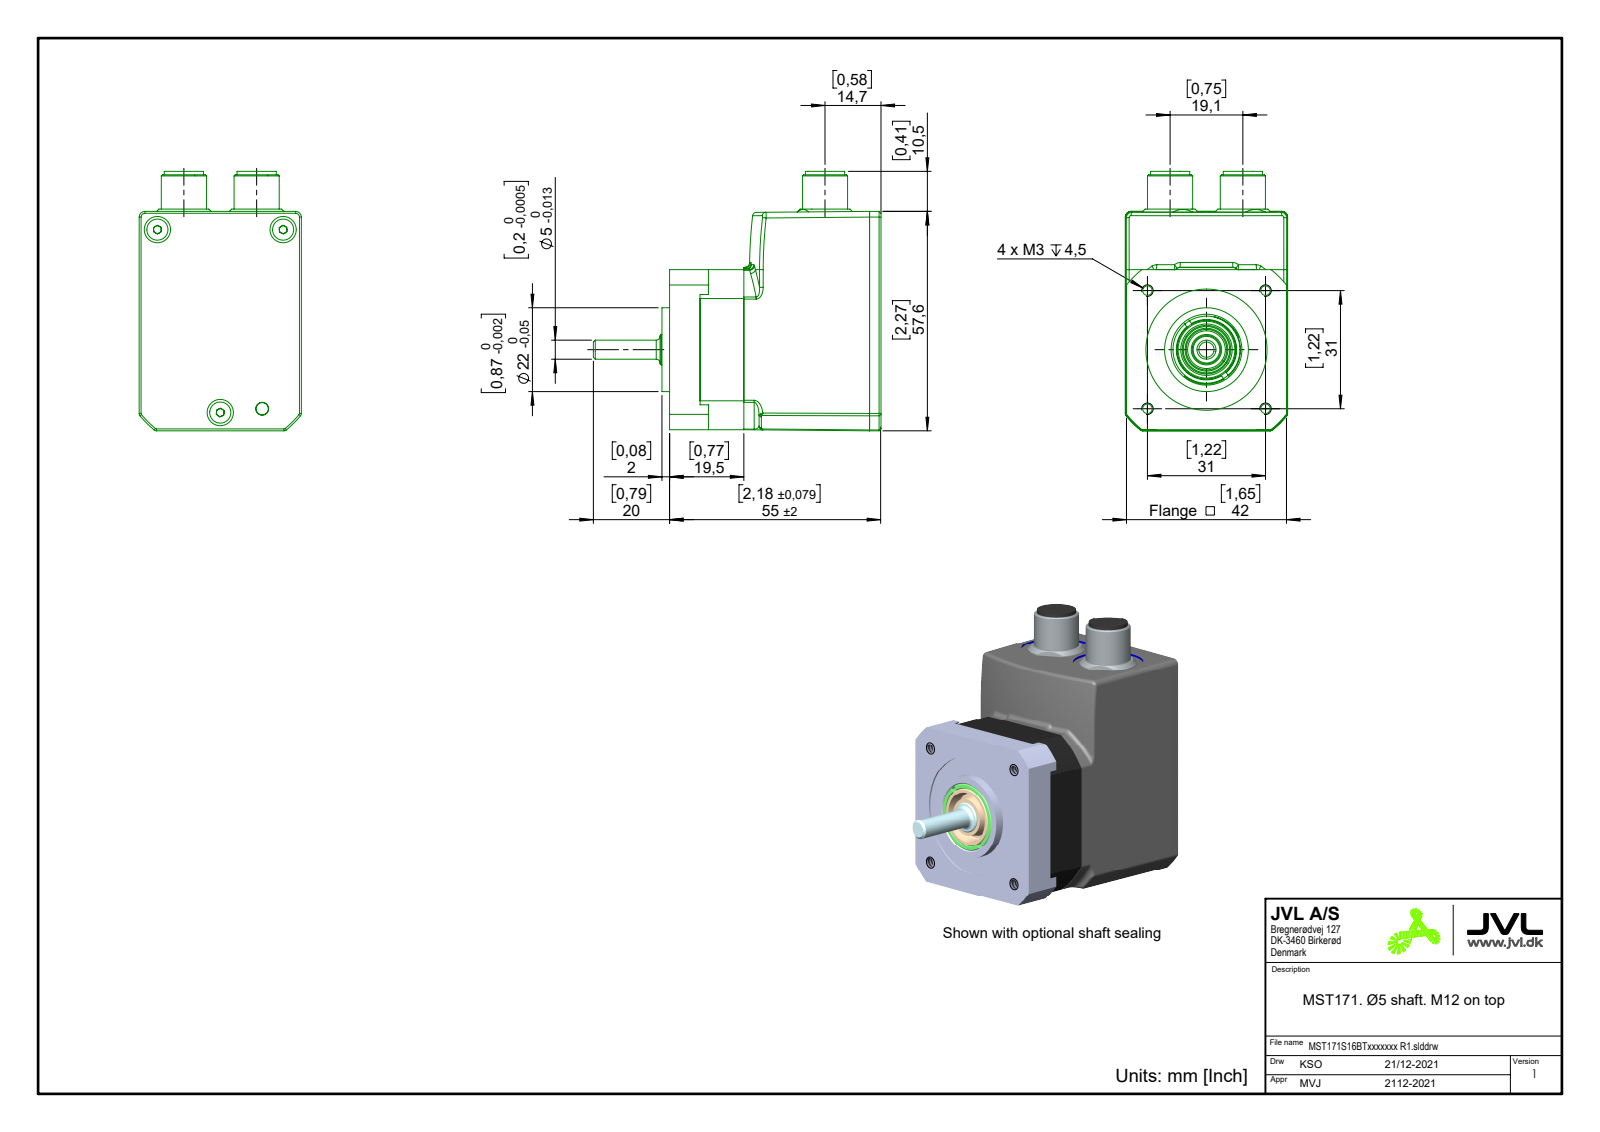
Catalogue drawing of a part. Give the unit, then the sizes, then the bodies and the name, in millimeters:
Units: millimetres
Overall size (bounding box): 75.5 × 68.08 × 42.58
Round holes (diameter × count): ⌀2.5 ×4, ⌀3.3 ×3, ⌀18.4 ×2, ⌀2.8 ×1, ⌀3.4 ×1, ⌀9 ×1, ⌀10 ×1, ⌀31.8 ×1
Round bosses / shafts (diameter × count): ⌀5.54 ×3, ⌀3 ×3, ⌀15.1 ×2, ⌀11.85 ×2, ⌀10.3 ×2, ⌀22 ×1, ⌀15.5 ×1, ⌀13.9 ×1
Partial cylindrical surfaces — rounded edges, fillets, slot ends (radius × count): R1 ×13, R1.5 ×2, R8.8 ×1, R24.92 ×1, R25.5 ×1, R27 ×1, R27.29 ×1, R80 ×1
Main face-to-face distances: 42, 55.5, 2, 55, 0.5, 42.29, 1.5, 53.5, 2.5, 4
Hole centre spacings: 21.92, 31, 35.56, 15.53, 16.03, 35.78, 43.84, 47.01
Volume: 119 899 mm³ · Surface area: 18 513 mm²
Bodies: 5 solids, 332 faces (135 planar, 73 cylindrical, 124 other)
Part name (STEP PRODUCT): MST171S16BTxxxxxxx
STEP written by: SolidWorks 2020 (AUTOMOTIVE_DESIGN)
